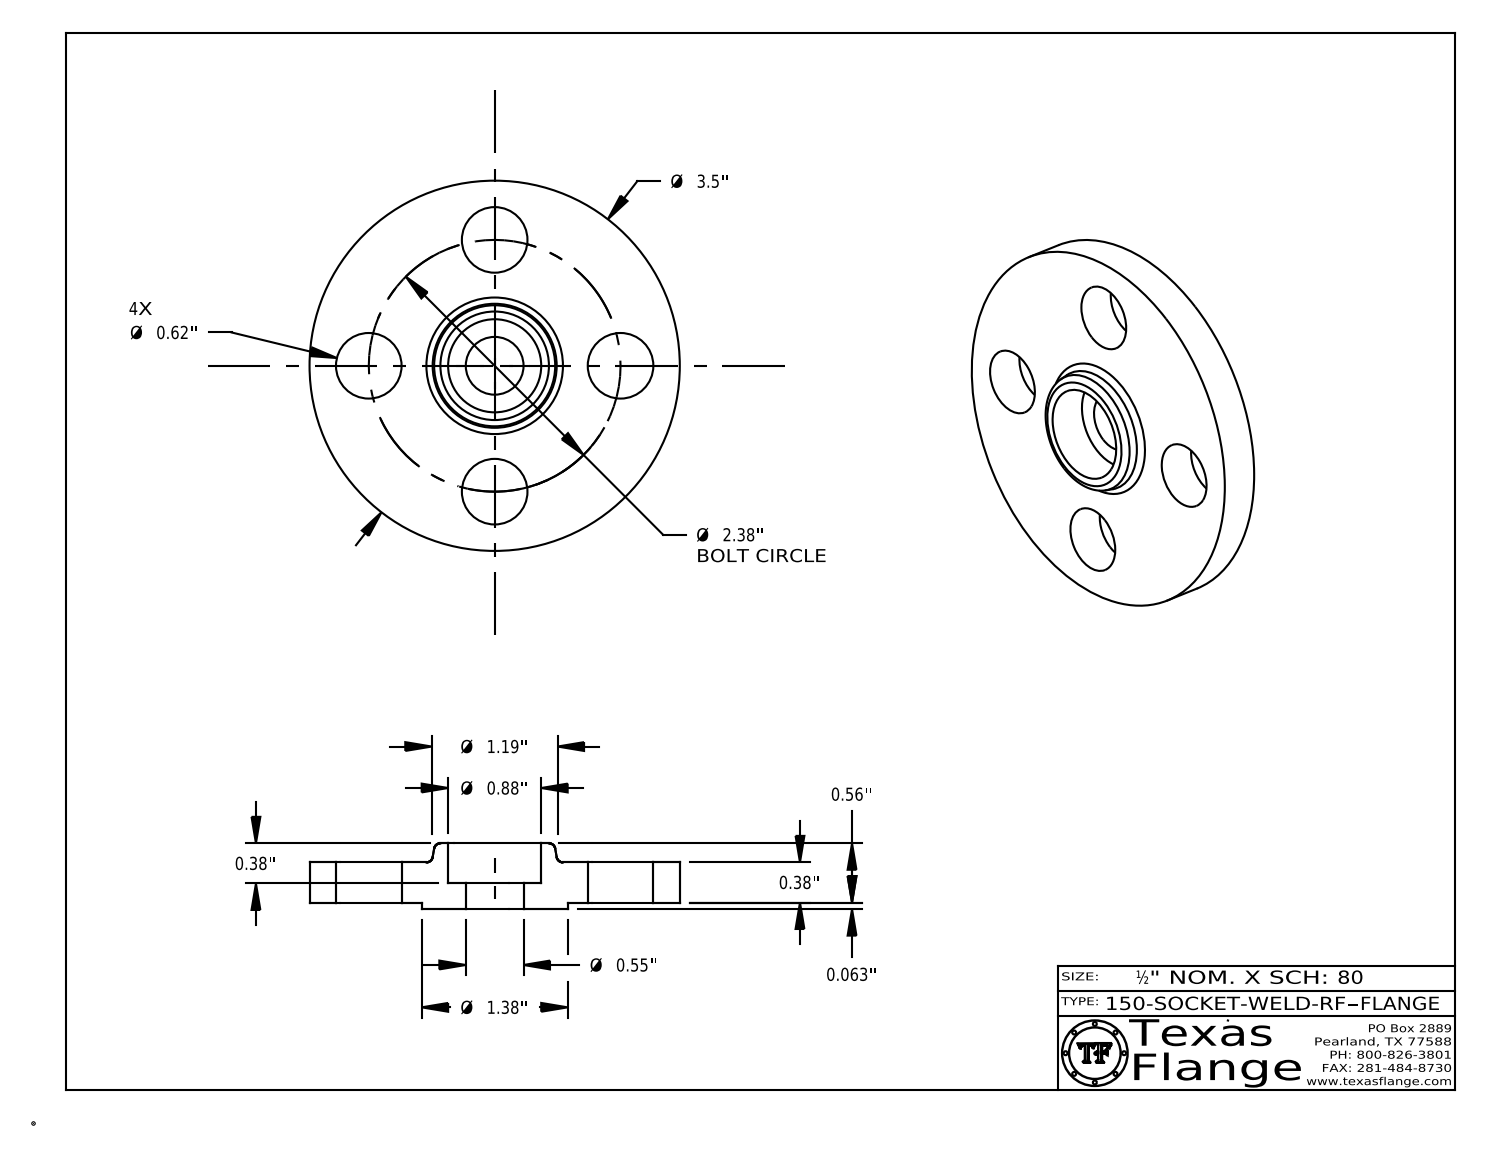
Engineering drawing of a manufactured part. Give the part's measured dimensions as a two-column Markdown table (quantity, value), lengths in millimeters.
| quantity | value |
| --- | --- |
| part name | 150-SOCKET-WELD-RF |
| STEP written by | CATIA V5 STEP AP214 (AUTOMOTIVE_DESIGN) |
| units | millimeters |
| bodies | 1 solid, 412 faces (370 planar, 36 cylindrical, 6 other) |
| overall size | 88.9 × 88.9 × 15.8 |
| volume | 52 290 mm³ |
| surface area | 16 610 mm² |
| round holes (diameter × count) | 15.7 × 4, 12.6 × 1, 13.9 × 1, 22.4 × 1 |
| round bosses / shafts (diameter × count) | 0.8 × 8, 88.9 × 1, 35.1 × 1, 9.9 × 1 |
| main face-to-face distances | 9.7, 1.6, 11.3, 4.6, 6.2, 5.1, 15.8, 14.2, 10.9, 9.3 |
| hole center spacings | 30.2, 42.7, 23.1, 55.9, 60.5, 30.2 |
